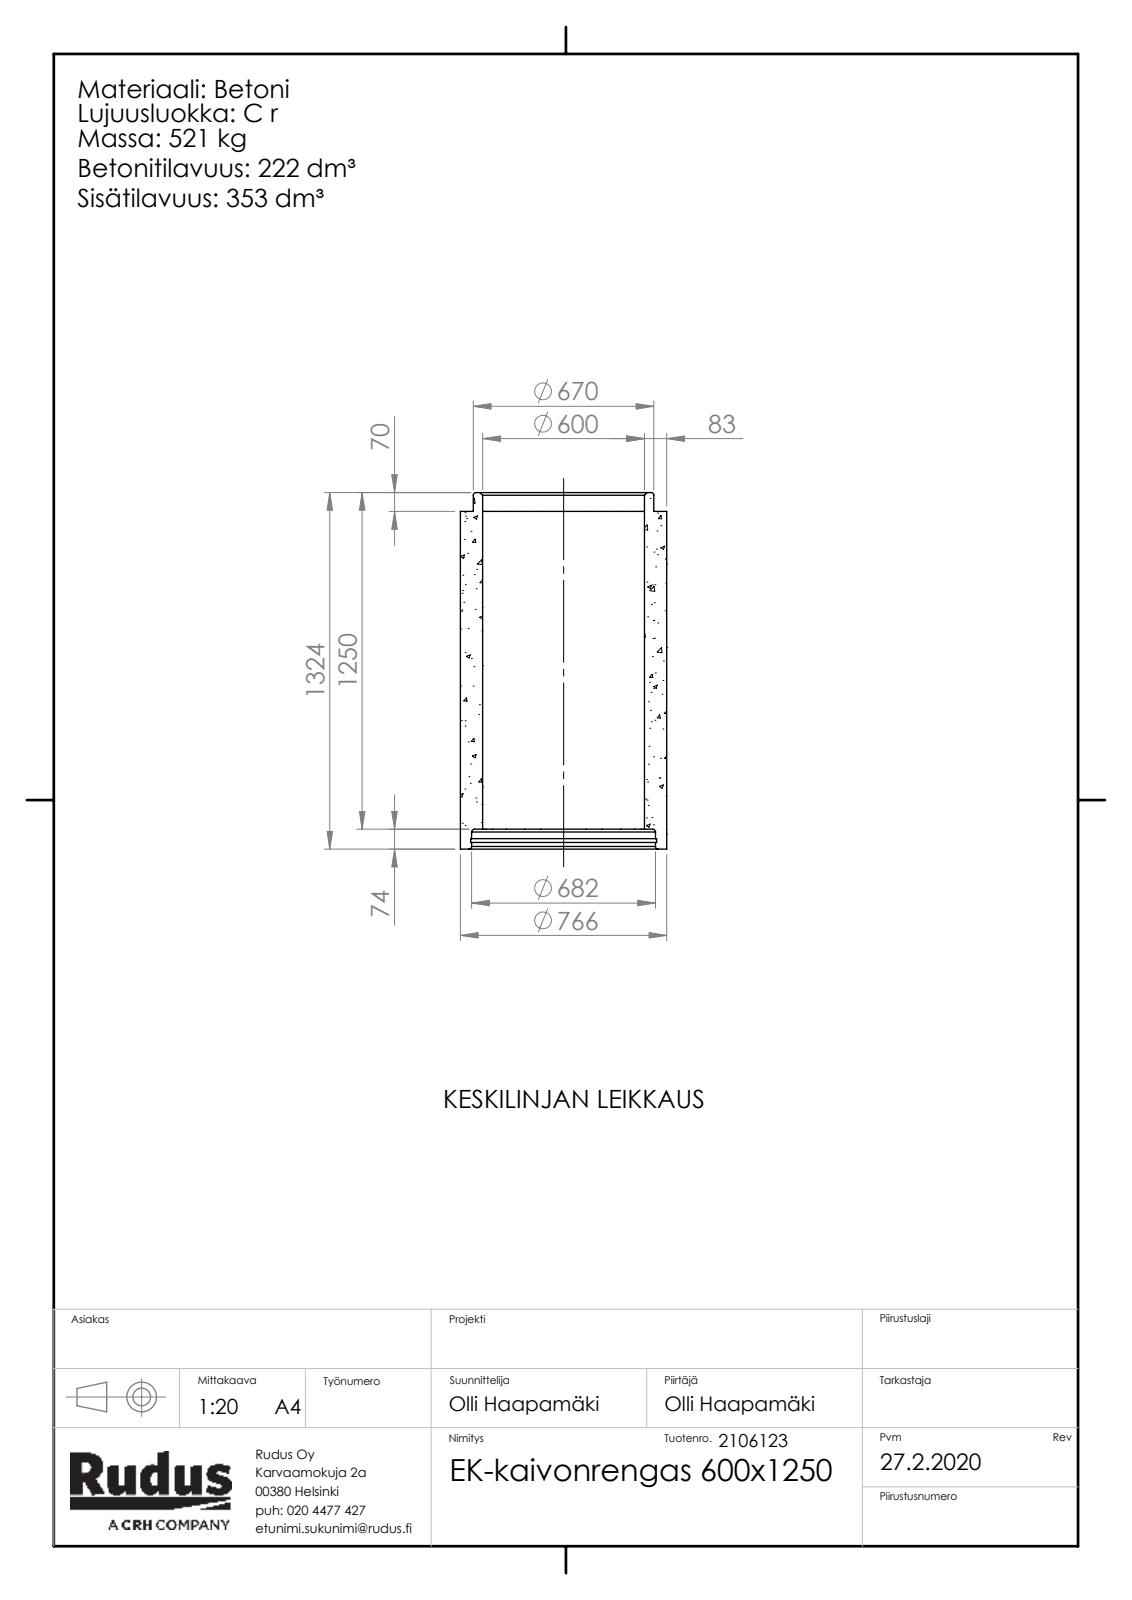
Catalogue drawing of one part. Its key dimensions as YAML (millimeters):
part_name: "Rudus 2106123 EK-kaivonrengas 600x1250; EK-osa-kaivorunko_EK-kaivonrengas"
step_written_by: "SolidWorks 2019 (CONFIG_CONTROL_DESIGN)"
units: millimeters
bodies: {solids: 1, faces: 107, planar: 6, cylindrical: 12, other: 89}
overall_size: [1324, 766, 766]
volume: 221900000
surface_area: 6020000
round_holes:
  - {diameter: 600, count: 1}
  - {diameter: 682, count: 1}
  - {diameter: 690, count: 1}
round_bosses_or_shafts:
  - {diameter: 766, count: 1}
  - {diameter: 670, count: 1}
face_to_face_distances: [1254, 74, 1180, 1324, 1250, 70, 25, 49, 1229, 1299]
